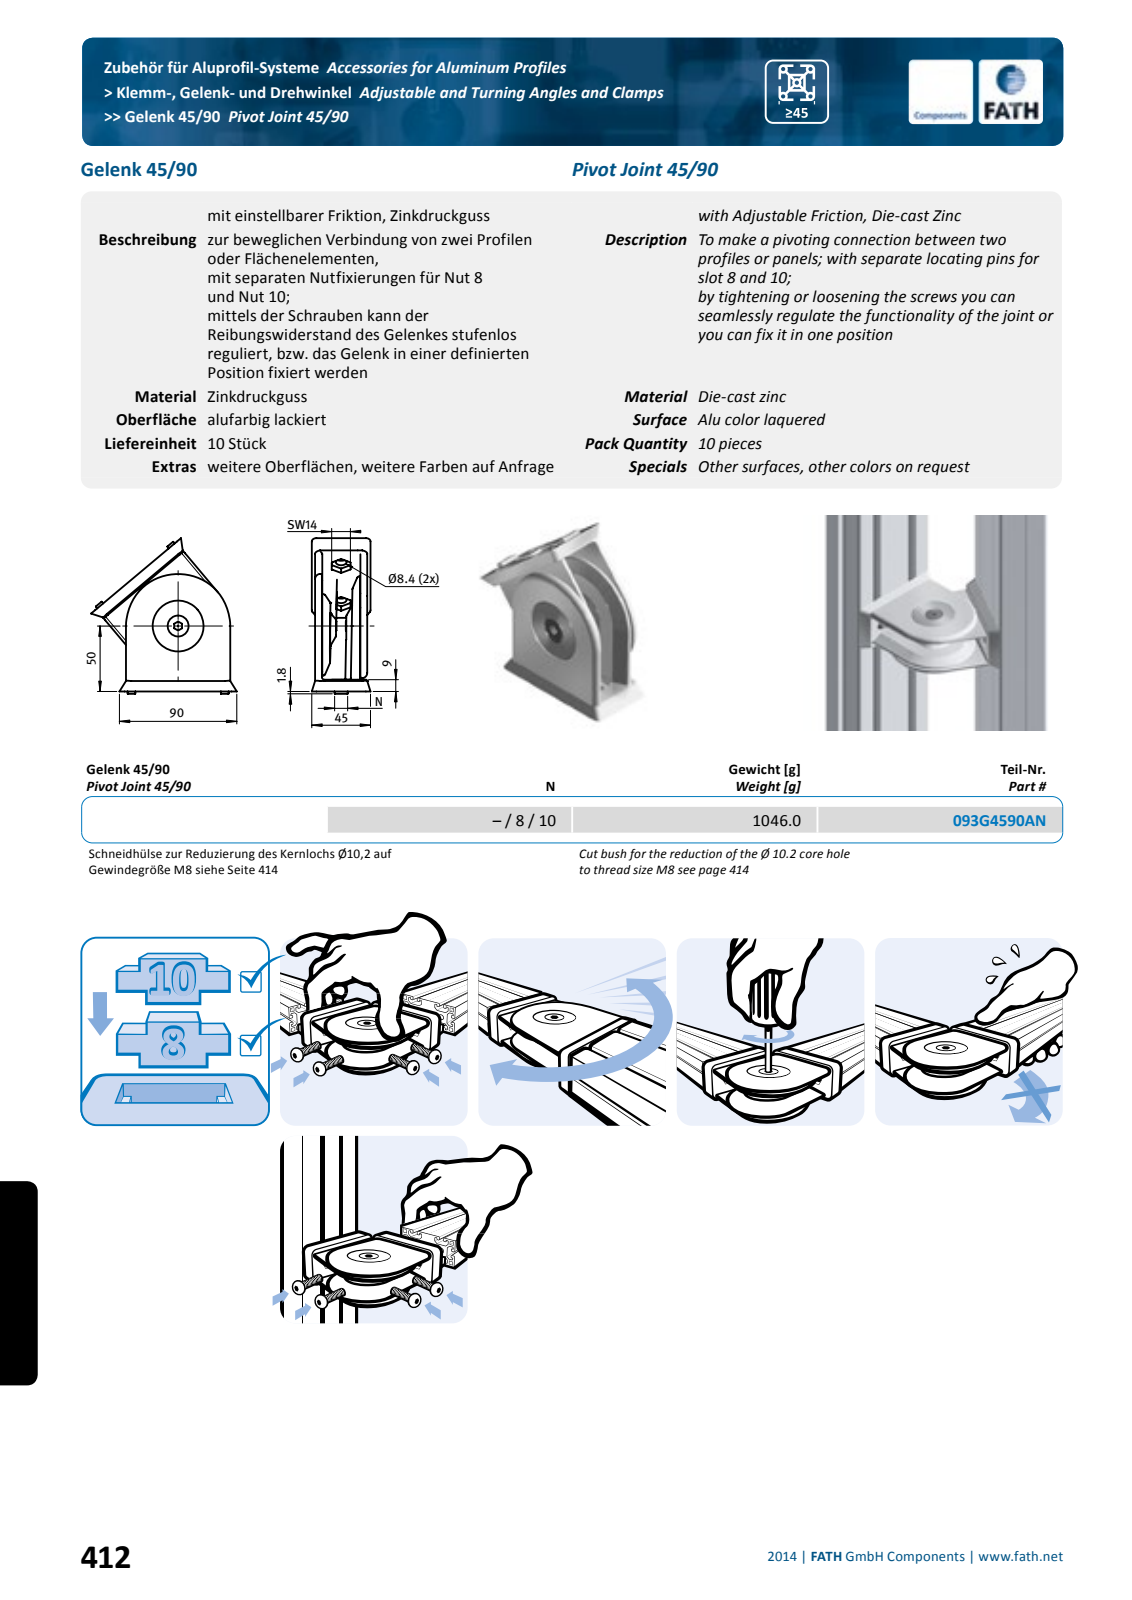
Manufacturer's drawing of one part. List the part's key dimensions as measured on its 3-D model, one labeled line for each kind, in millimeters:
Part name (STEP PRODUCT): fath_093g4590an_1; fath_093g4590an_2; fath_093g4590an_3; fath_093g4590an_4 (+4 more)
STEP written by: Spatial InterOp 3D (automotive_design)
Units: millimetres
Bodies: 8 solids, 566 faces (178 planar, 160 cylindrical, 228 other)
Overall size (bounding box): 117.1 × 111.26 × 44.8
Volume: 188 010 mm³ · Surface area: 78 928 mm²
Round holes (diameter × count): ⌀6.8 ×1, ⌀9 ×1, ⌀20 ×1, ⌀60.4 ×1, ⌀70 ×1
Round bosses / shafts (diameter × count): ⌀2 ×4, ⌀79.6 ×1, ⌀75.6 ×1, ⌀69.6 ×1, ⌀60 ×1, ⌀40 ×1, ⌀28 ×1, ⌀16 ×1
Partial cylindrical surfaces — rounded edges, fillets, slot ends (radius × count): R1 ×44, R2 ×18, R4 ×12, R1.5 ×4, R2.5 ×4
Main face-to-face distances: 5.2, 29.1, 5.5, 34.3, 34.6, 29.4, 34.5, 28.8, 39.8, 6.5
